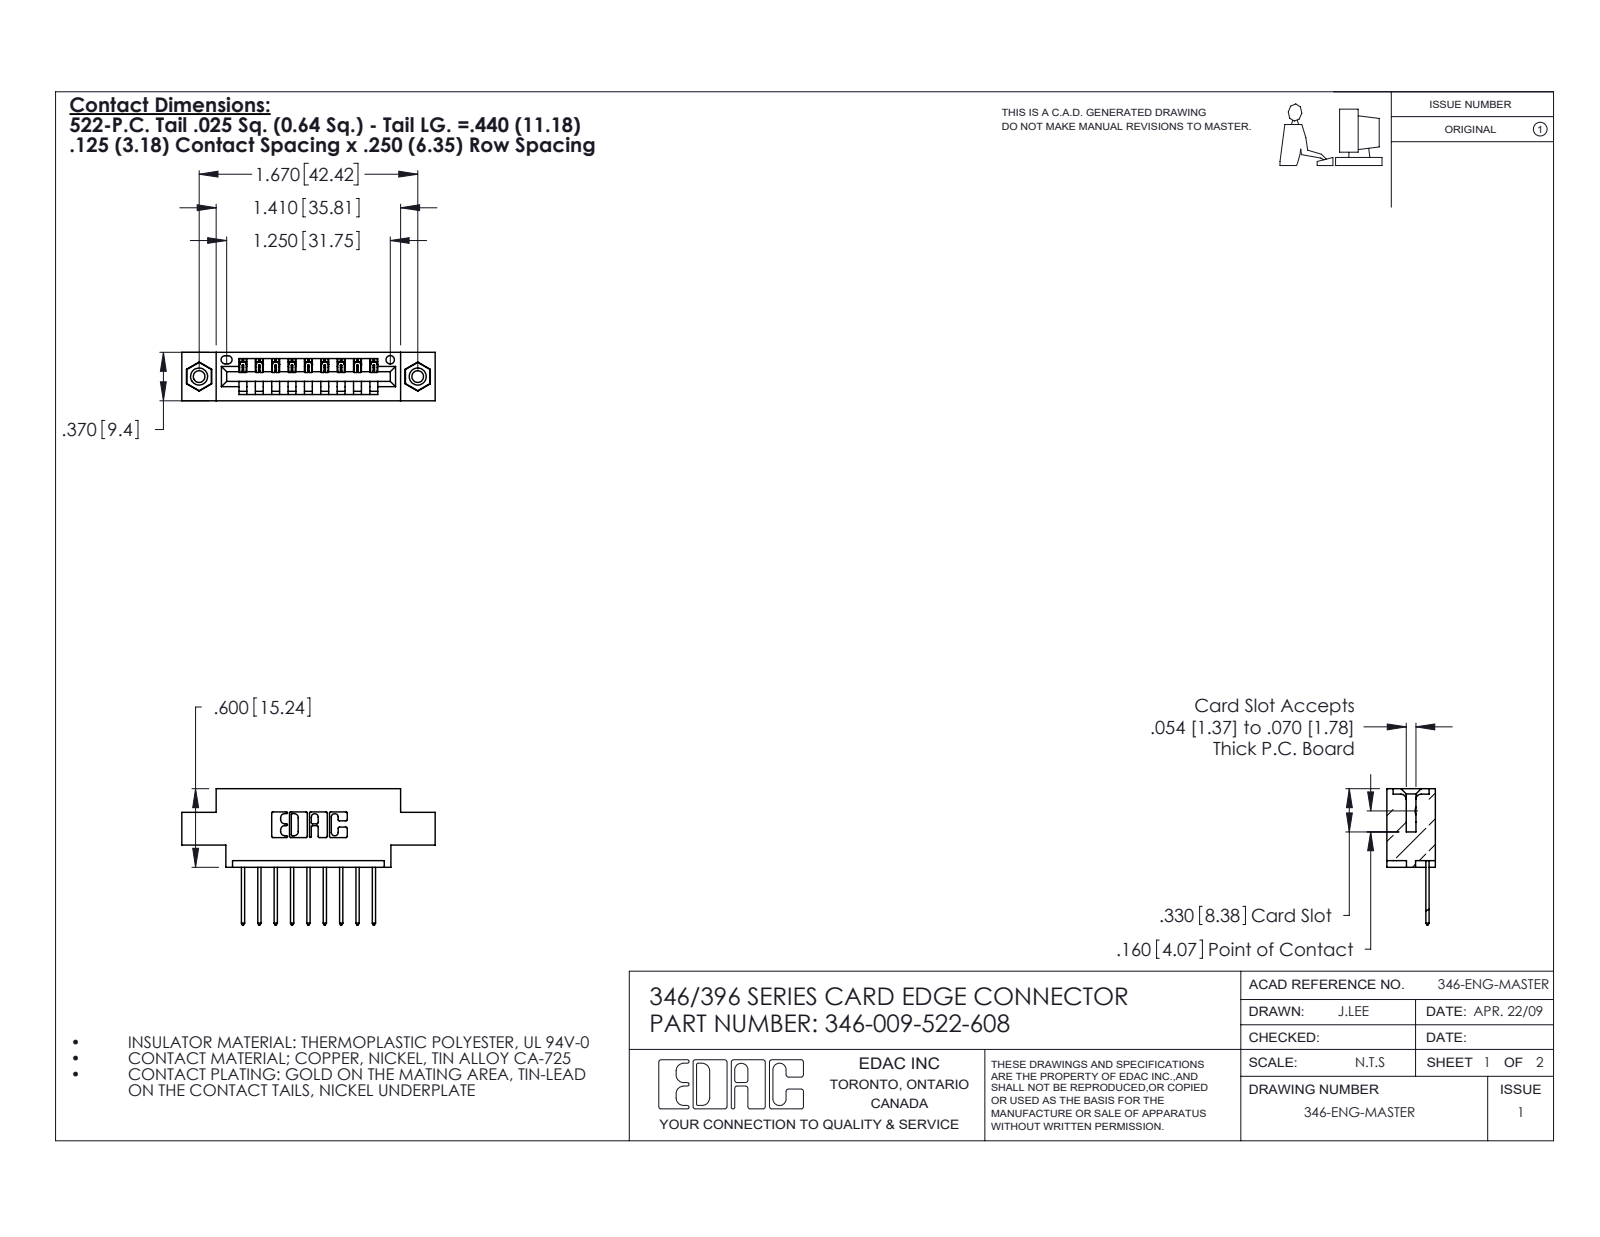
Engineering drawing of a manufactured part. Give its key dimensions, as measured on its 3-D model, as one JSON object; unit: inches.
{"part_name": "345-250-001_345-250-003-102; 346-009-522-608; 346 Part_0.170 Offset - 0.156 Dia-TI; 345-292-001_345-293-122", "step_written_by": "SolidWorks 2020 (CONFIG_CONTROL_DESIGN)", "units": "inches", "bodies": {"solids": 12, "faces": 708, "planar": 472, "cylindrical": 220, "other": 16}, "overall_size": [1.935, 1.04, 0.37], "volume_in3": 0.263, "surface_area_in2": 8.146, "round_holes": [[0.089, 2], [0.125, 2], [0.156, 2], [0.064, 1]], "round_bosses_or_shafts": [[0.155, 2]], "partial_cylinders_radius": [[0.01, 22], [0.006, 18], [0.01, 18], [0.007, 6], [0.031, 6], [0.026, 3], [0.031, 2], [0.04, 2]], "face_to_face_distances": [0.25, 0.37, 0.048, 0.322, 0.222, 0.072, 0.298, 0.025, 0.148, 0.1], "hole_center_spacings": [0.246, 1.465, 1.67]}
